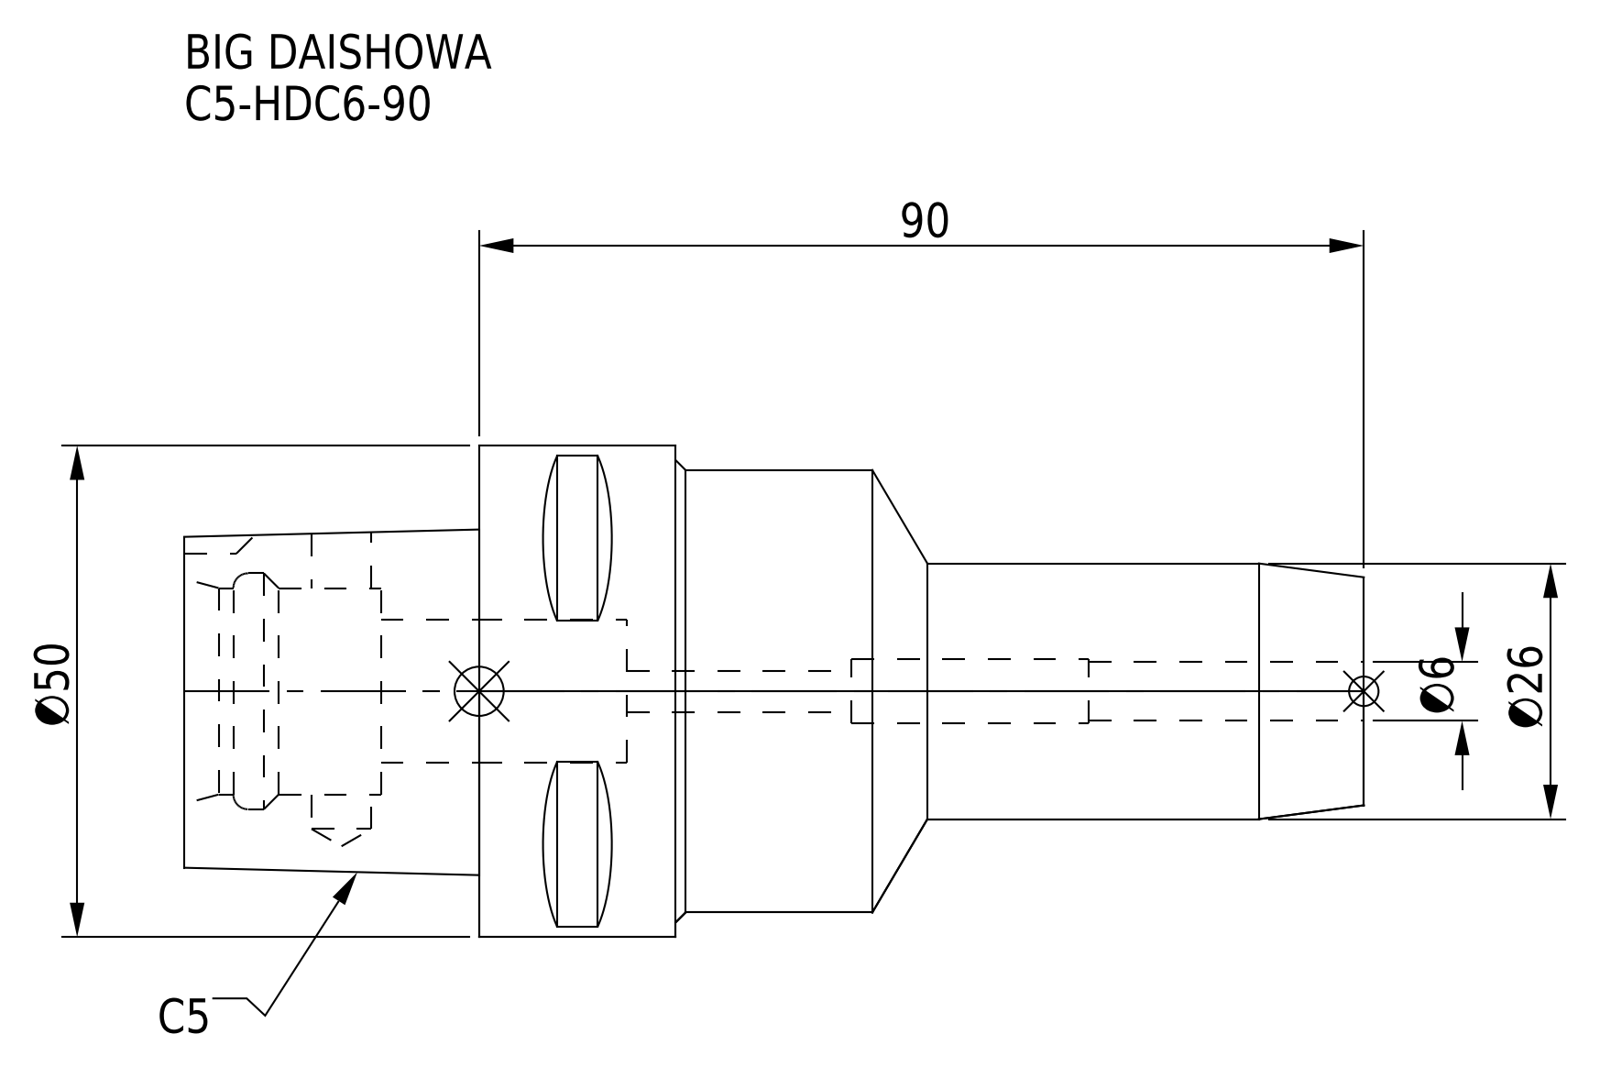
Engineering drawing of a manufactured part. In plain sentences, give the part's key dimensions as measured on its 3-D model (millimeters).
The part is named "C5-HDC6-90". Its 3-D file was written by "CREO PARAMETRIC BY PTC INC, 2016380 (AUTOMOTIVE_DESIGN)". It is 1 solid with 71 faces: 30 planar, 25 cylindrical and 16 other. Overall it measures 120 by 50 by 50 millimeters. Its volume is 112 627 cubic millimeters and its surface area 20 810 square millimeters. Round holes: 1 of diameter 4.2, 1 of diameter 6, 1 of diameter 6.1, 1 of diameter 6.5, 1 of diameter 14.5, 1 of diameter 21, 1 of diameter 24. Round bosses or shafts: 1 of diameter 50, 1 of diameter 45, 1 of diameter 26. Partial cylindrical surfaces (rounded edges, fillets, slot ends): 1 of radius 4. The main face-to-face distances are 30, 20, 90, 120, 70, 50, 44, 100, 10, 75.
